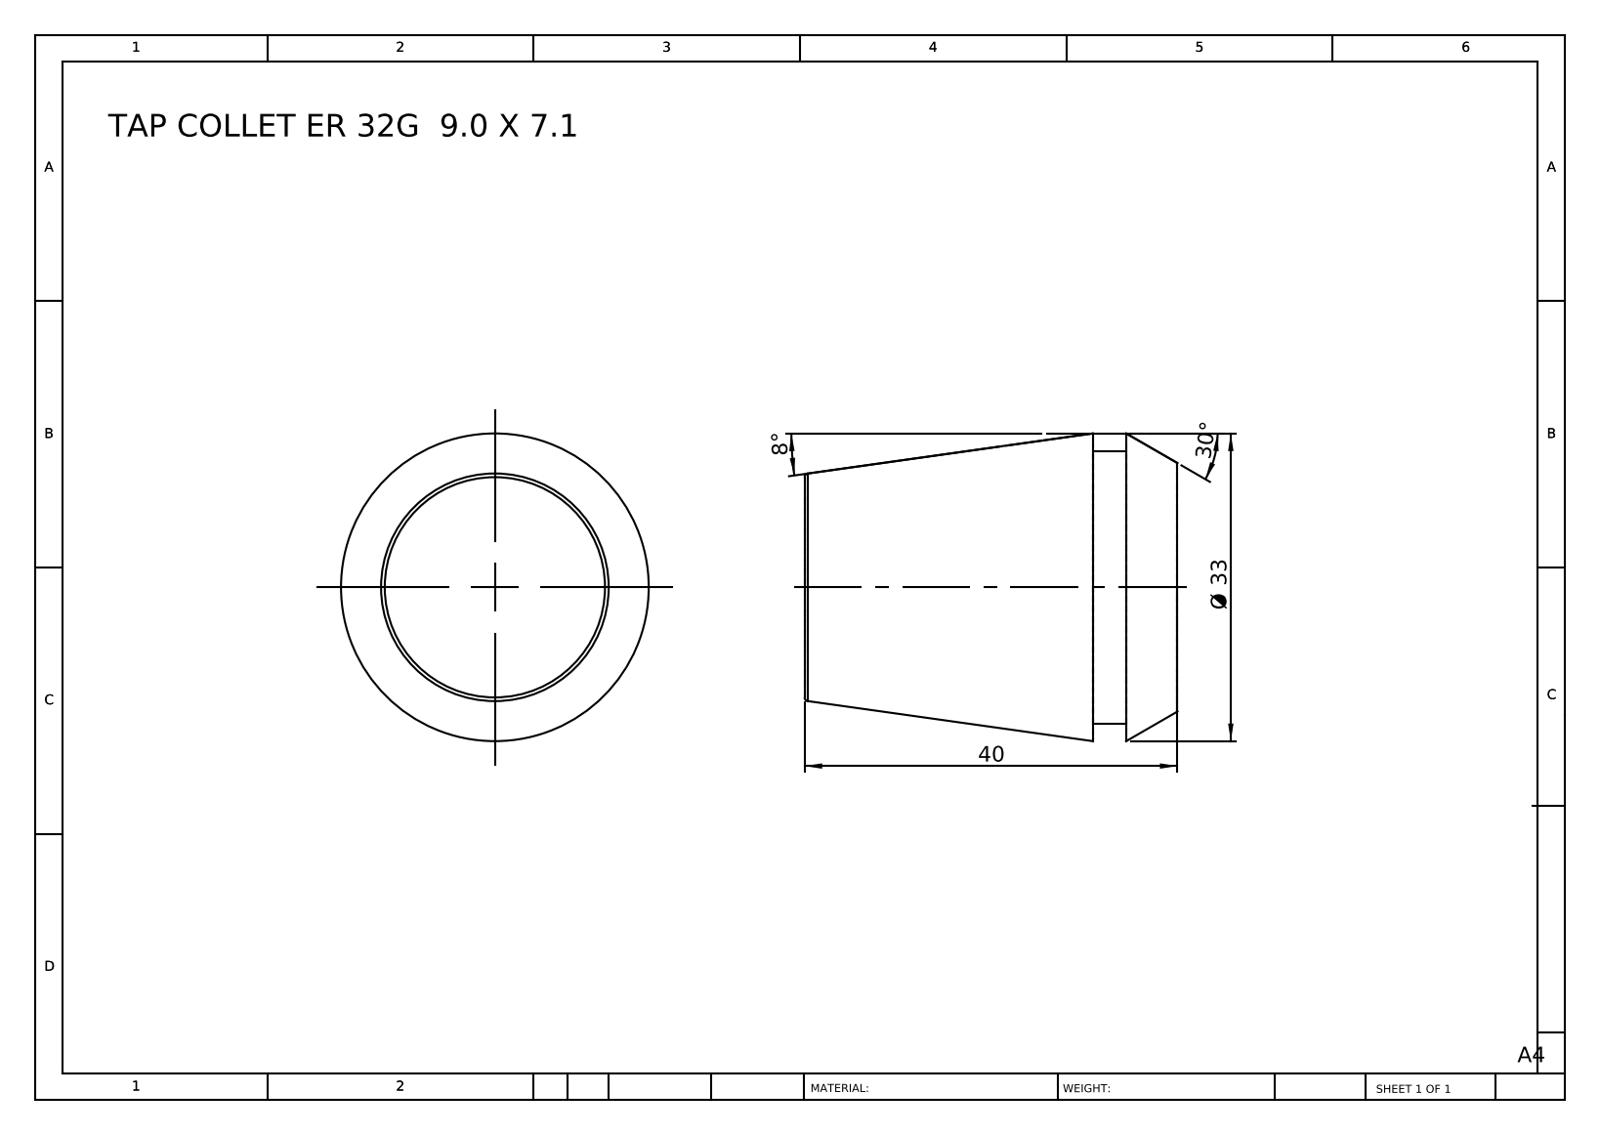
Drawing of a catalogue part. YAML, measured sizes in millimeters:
part_name: "TAP COLLET ER 32G 9.0 X 7.1"
step_written_by: "SolidWorks 2014 (CONFIG_CONTROL_DESIGN)"
units: millimeters
bodies: {solids: 1, faces: 12, planar: 4, cylindrical: 2, other: 6}
overall_size: [40, 33, 33]
volume: 26350
surface_area: 5119
round_bosses_or_shafts:
  - {diameter: 29.2, count: 1}
face_to_face_distances: [40, 9.1, 30.9, 5.5, 3.6, 34.5]
